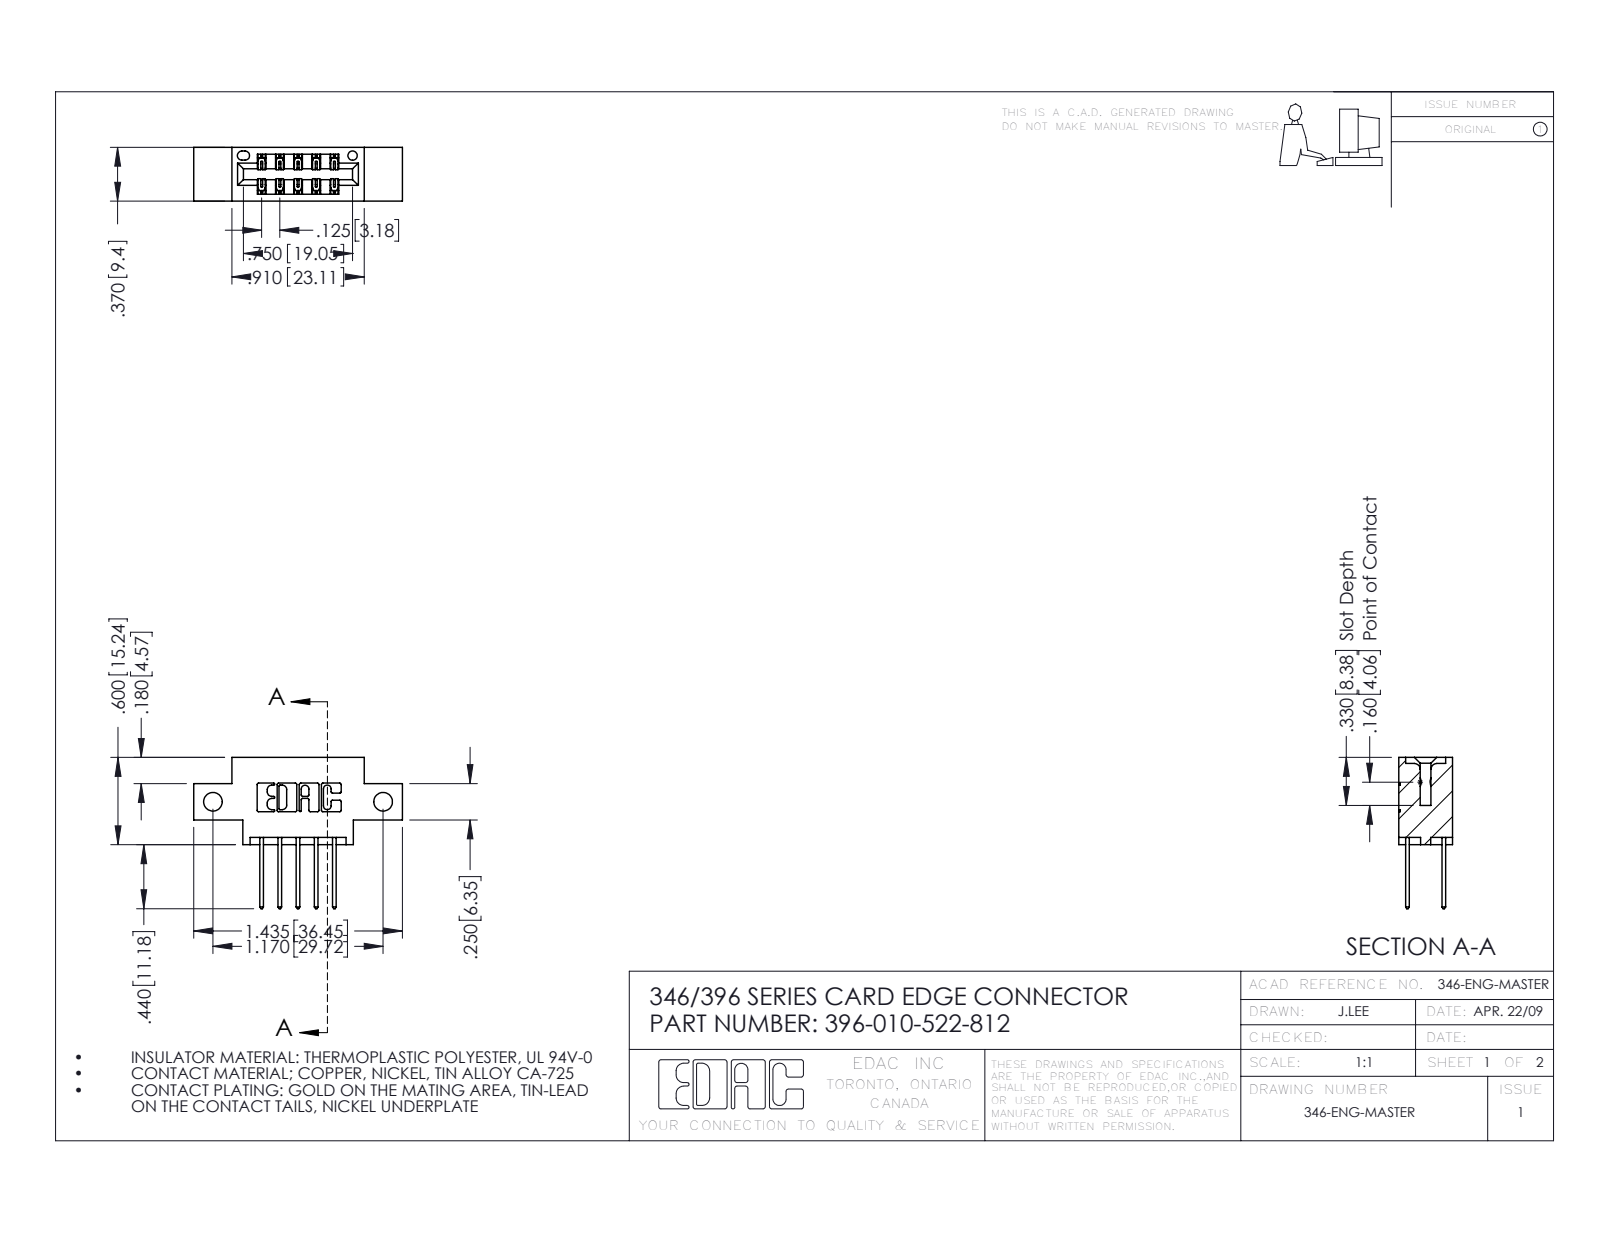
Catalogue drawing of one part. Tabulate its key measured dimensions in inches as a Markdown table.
| quantity | value |
| --- | --- |
| part name | 396-010-522-812; 345-292-001_345-293-122; 346 Part_0.170 Offset - Side Mount |
| STEP written by | SolidWorks 2016 (CONFIG_CONTROL_DESIGN) |
| units | inches |
| bodies | 11 solids, 646 faces (430 planar, 216 cylindrical, 0 other) |
| overall size | 1.435 × 1.04 × 0.37 |
| volume | 0.186 in³ |
| surface area | 5.848 in² |
| round holes (diameter × count) | 0.128 × 2, 0.064 × 1 |
| partial cylindrical surfaces (radius × count) | 0.01 × 22, 0.006 × 15, 0.01 × 10, 0.007 × 6, 0.031 × 6, 0.026 × 3, 0.014 × 2, 0.022 × 2 |
| main face-to-face distances | 0.25, 0.37, 0.048, 0.322, 0.025, 0.072, 0.298, 0.275, 0.225, 0.148 |
| hole center spacings | 1.17 |
